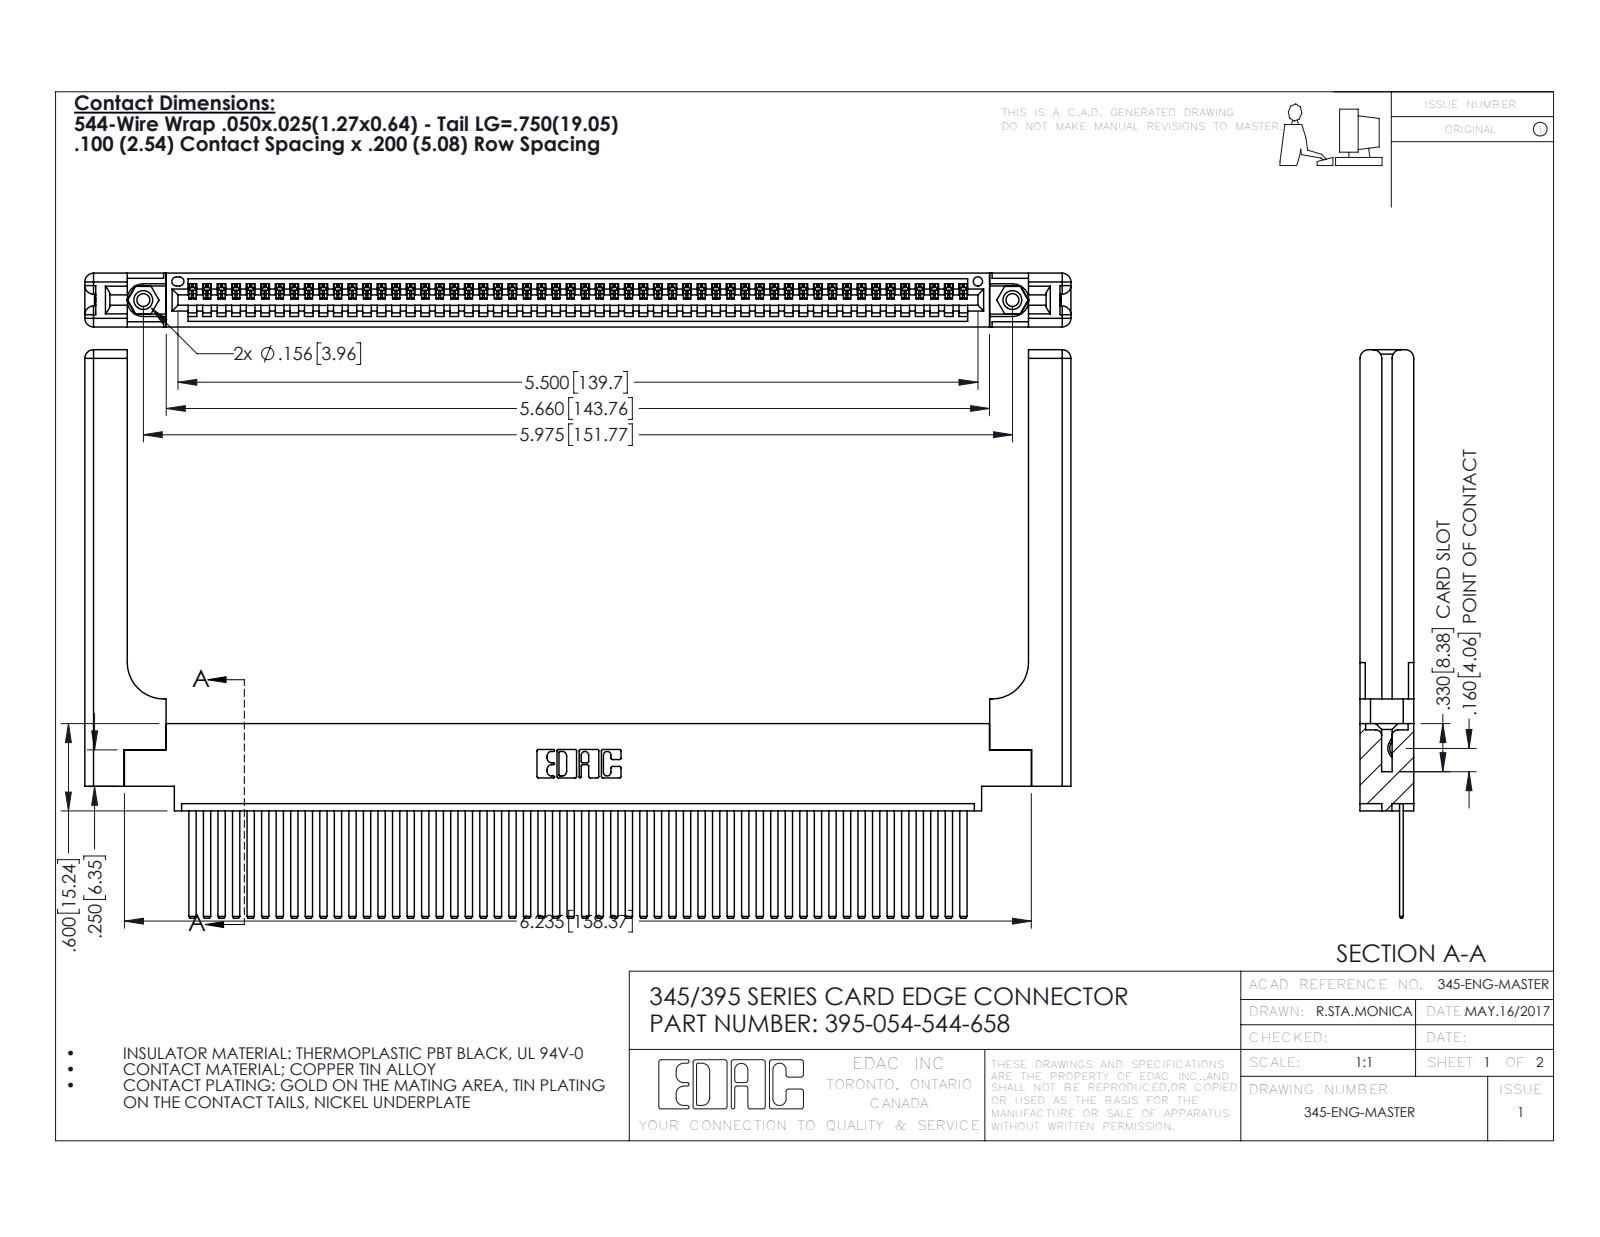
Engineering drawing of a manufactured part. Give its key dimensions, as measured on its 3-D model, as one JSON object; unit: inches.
{"part_name": "345-250-001_345-250-001-102; 345-292-001_345-293-144; 345-220-058_345-220-058; 345 Part_0.170 Offset - 0.156 Dia-TH (+1 more)", "step_written_by": "SolidWorks 2016 (CONFIG_CONTROL_DESIGN)", "units": "inches", "bodies": {"solids": 59, "faces": 3194, "planar": 2176, "cylindrical": 958, "other": 60}, "overall_size": [6.779, 3.907, 0.37], "volume_in3": 1.554, "surface_area_in2": 46.53, "round_holes": [[0.089, 2], [0.125, 2], [0.156, 2], [0.064, 1]], "round_bosses_or_shafts": [[0.155, 2]], "partial_cylinders_radius": [[0.006, 108], [0.01, 22], [0.06, 16], [0.007, 6], [0.031, 6], [0.026, 3], [0.03, 2], [0.031, 2]], "face_to_face_distances": [0.072, 0.298, 0.37, 0.098, 0.272, 0.025, 0.2, 0.225, 0.148, 0.15], "hole_center_spacings": [0.27, 5.739, 5.975]}
